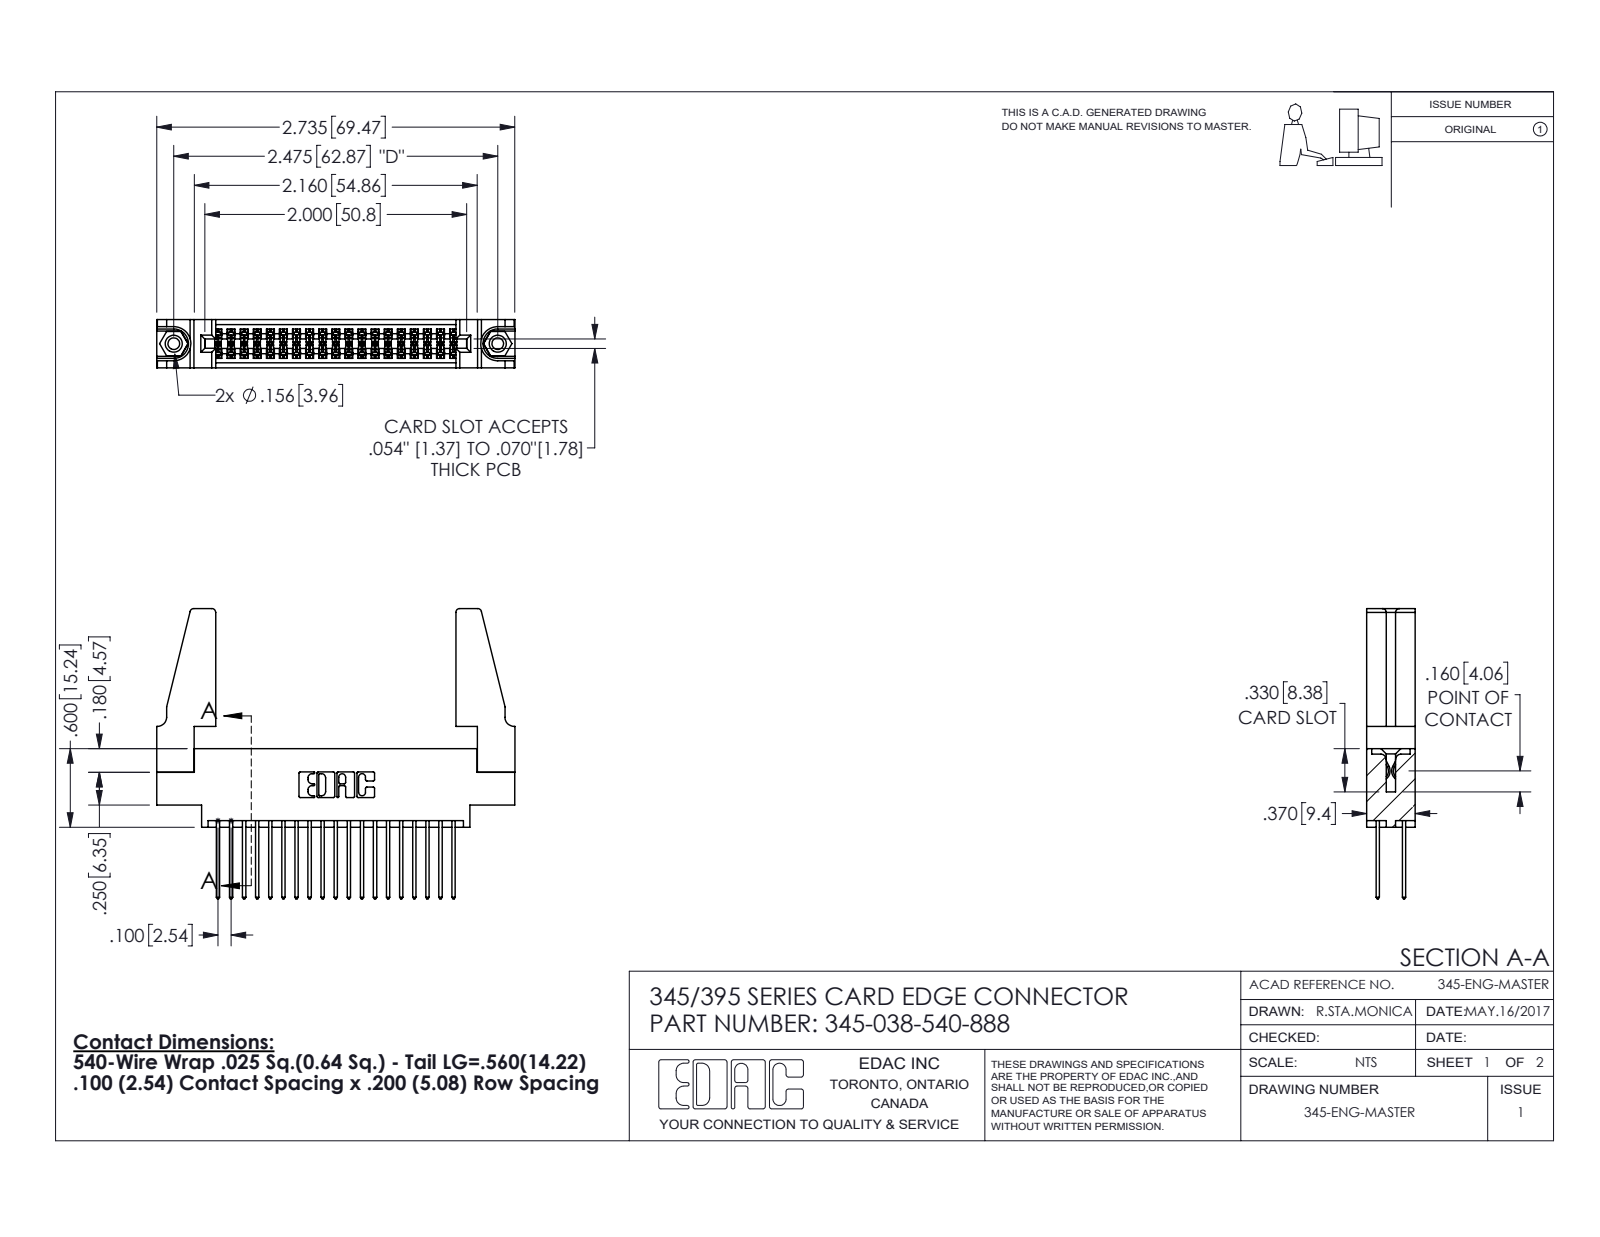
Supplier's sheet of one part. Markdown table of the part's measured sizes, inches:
| quantity | value |
| --- | --- |
| part name | 345 Part_0.170 Offset - 0.156 Dia-TH; 345-250-001_345-250-001-102; 345-292-001_345-293-140; 345-038-540-888 (+1 more) |
| STEP written by | SolidWorks 2016 (CONFIG_CONTROL_DESIGN) |
| units | inches |
| bodies | 43 solids, 2154 faces (1410 planar, 728 cylindrical, 16 other) |
| overall size | 2.736 × 2.217 × 0.37 |
| volume | 0.599 in³ |
| surface area | 20.46 in² |
| round holes (diameter × count) | 0.089 × 2, 0.125 × 2, 0.156 × 2, 0.064 × 1 |
| round bosses / shafts (diameter × count) | 0.155 × 2 |
| partial cylindrical surfaces (radius × count) | 0.006 × 57, 0.01 × 38, 0.01 × 22, 0.03 × 8, 0.007 × 6, 0.031 × 6, 0.026 × 3, 0.014 × 2 |
| main face-to-face distances | 0.072, 0.37, 0.298, 0.2, 0.098, 0.272, 0.025, 0.225, 0.175, 0.148 |
| hole center spacings | 0.27, 2.241, 2.475 |
